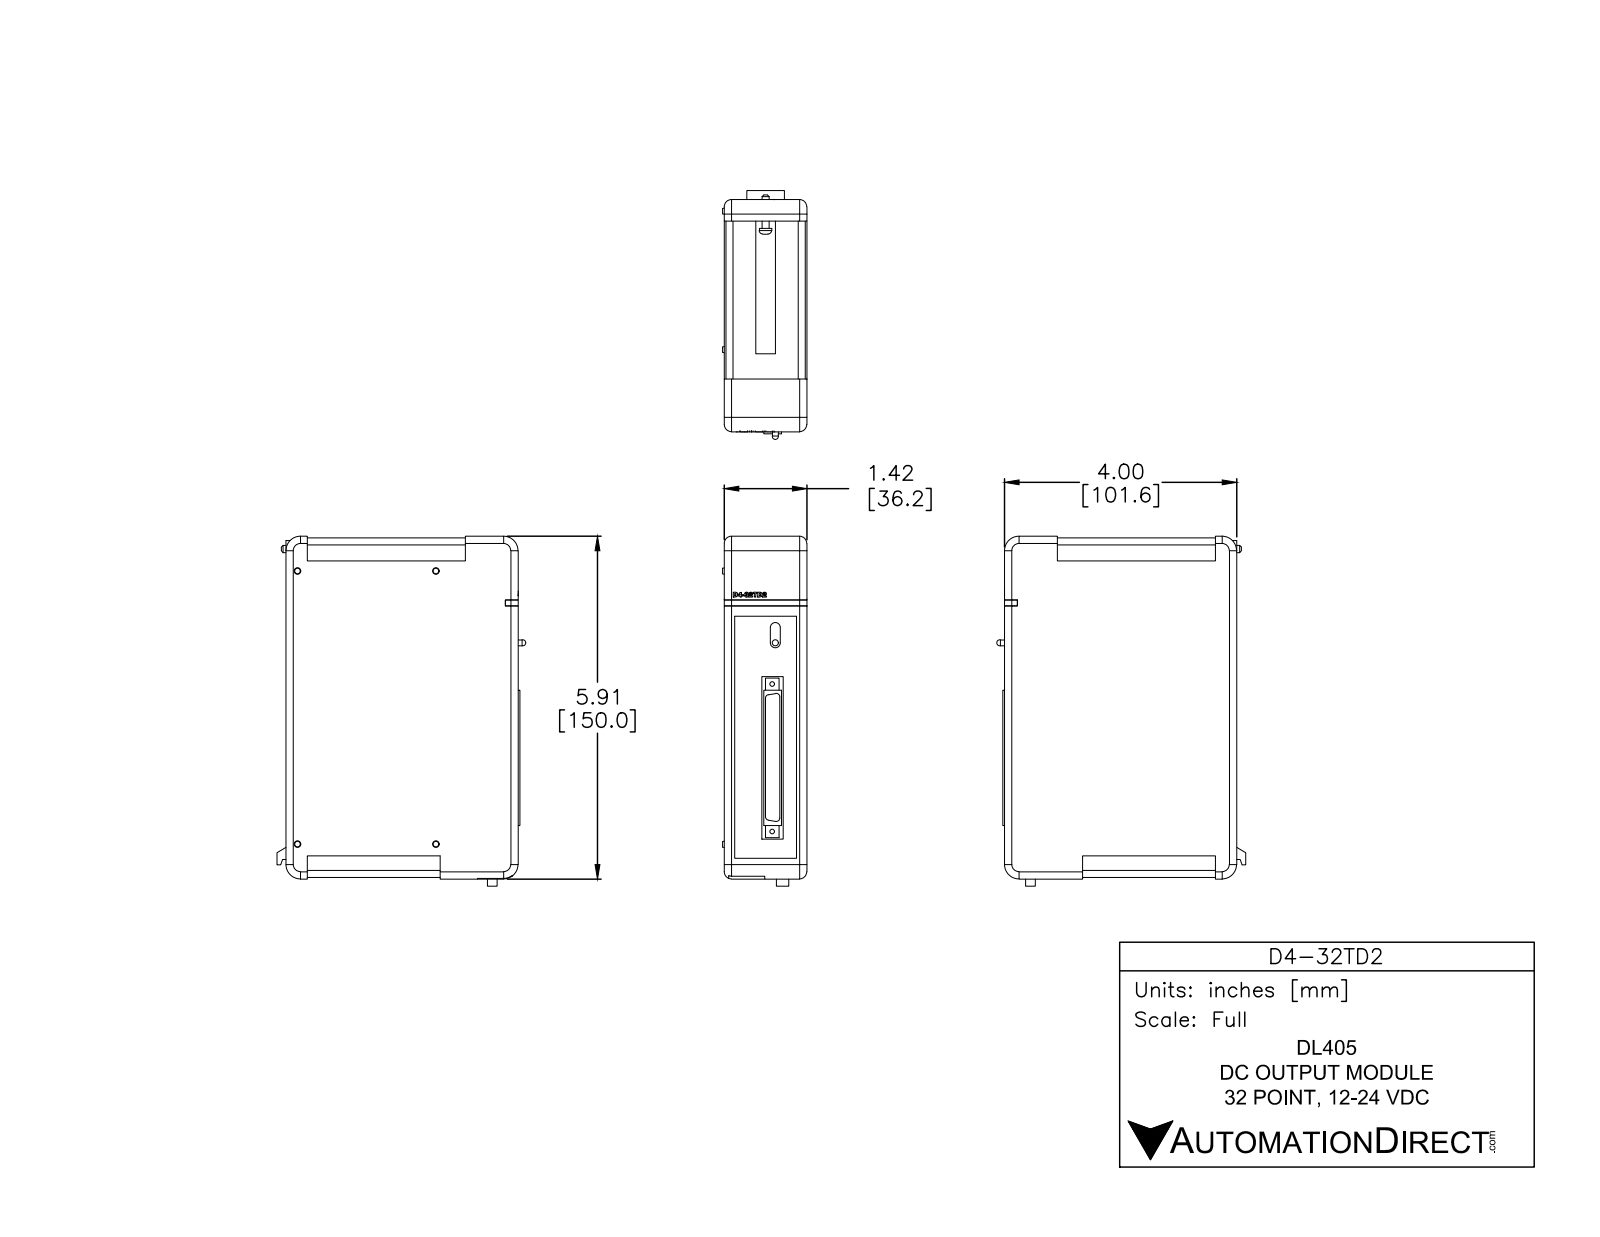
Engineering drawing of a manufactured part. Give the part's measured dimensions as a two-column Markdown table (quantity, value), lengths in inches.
| quantity | value |
| --- | --- |
| part name | D4-32TD2 |
| STEP written by | SolidWorks 2014 (AUTOMOTIVE_DESIGN) |
| units | inches |
| bodies | 2 solids, 301 faces (185 planar, 46 cylindrical, 70 other) |
| overall size | 6.025 × 4.285 × 1.455 |
| volume | 32.07 in³ |
| surface area | 83.59 in² |
| round holes (diameter × count) | 0.08 × 2 |
| round bosses / shafts (diameter × count) | 0.212 × 1, 0.123 × 1, 0.1 × 1 |
| partial cylindrical surfaces (radius × count) | 0.125 × 8, 0.06 × 4, 0.12 × 4, 0.25 × 4, 0.085 × 2, 0.145 × 1, 0.171 × 1 |
| main face-to-face distances | 1.425, 0.03, 3.97, 1.395, 5.845, 5.875, 4, 0.2, 3.77, 3.8 |
| hole center spacings | 2.538 |
